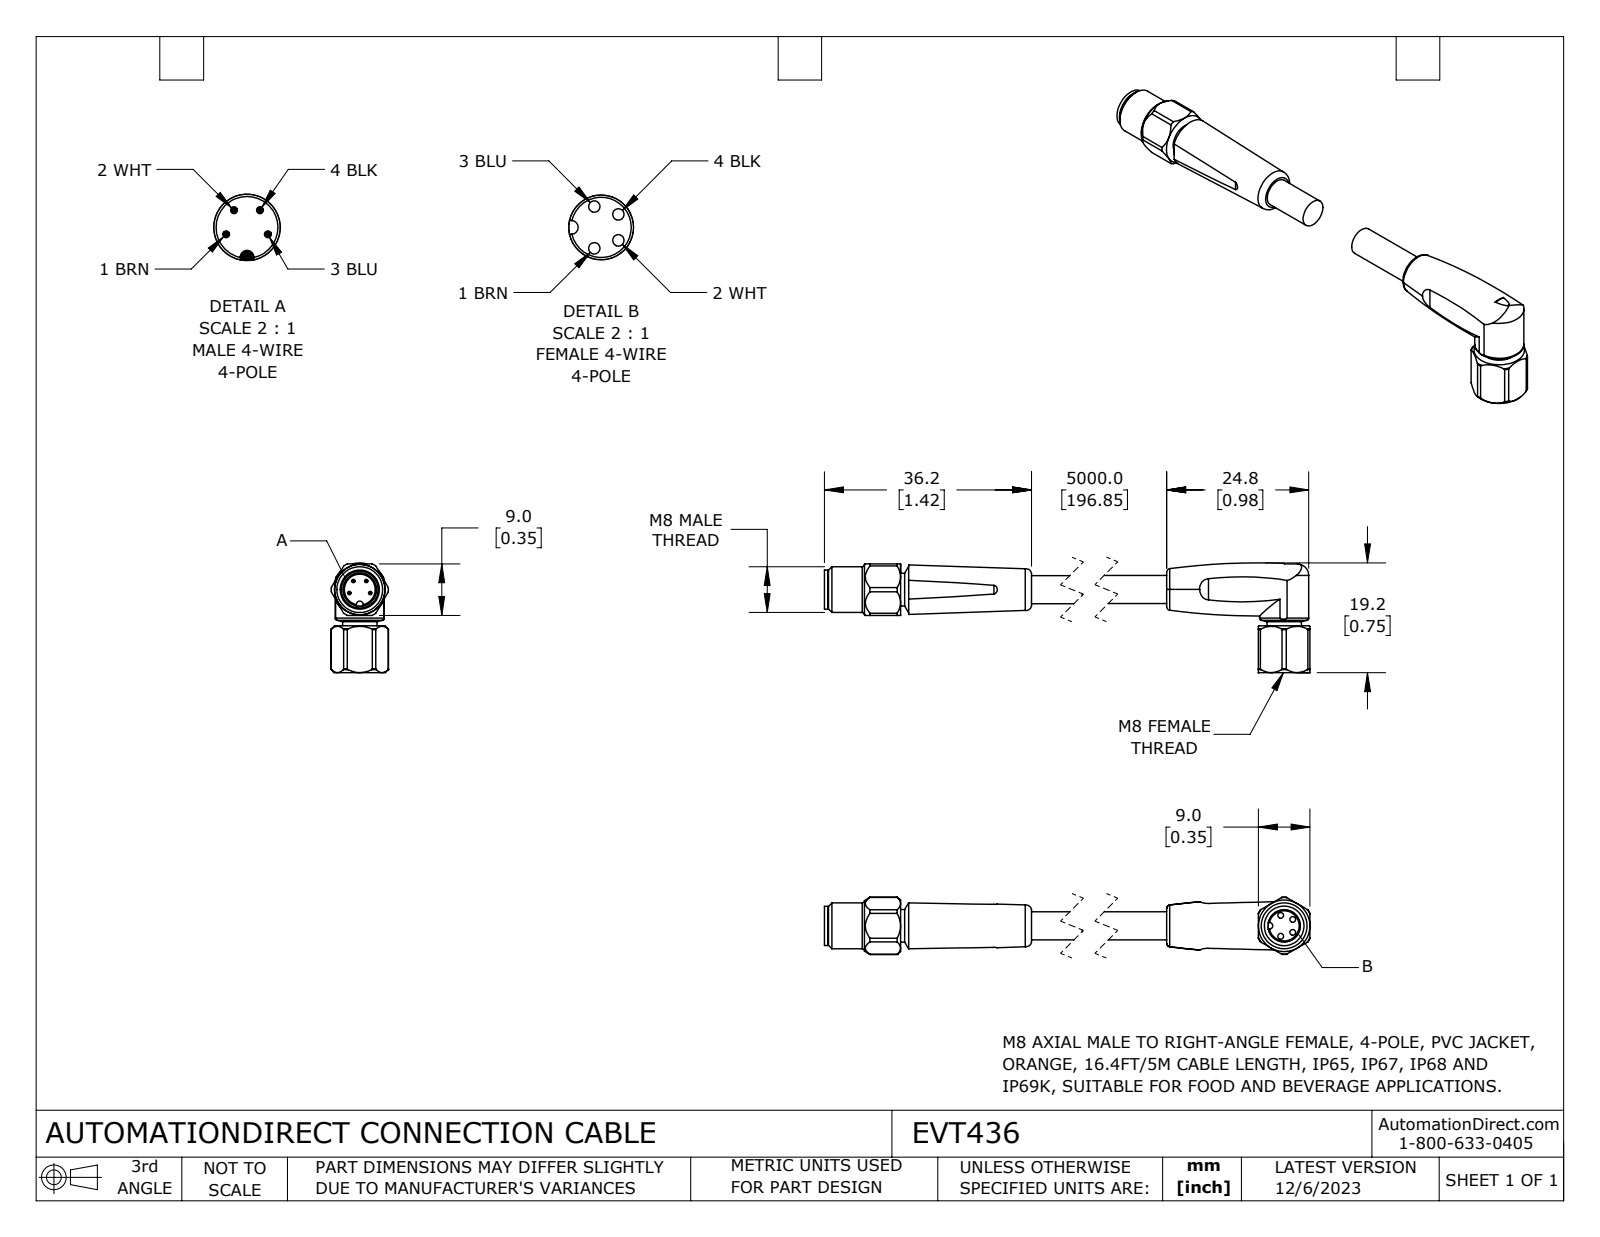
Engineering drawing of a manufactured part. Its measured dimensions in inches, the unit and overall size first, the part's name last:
Units: inches
Overall size (bounding box): 3.76 × 0.755 × 0.394
Round holes (diameter × count): ⌀0.039 ×4, ⌀0.228 ×1, ⌀0.272 ×1
Round bosses / shafts (diameter × count): ⌀0.023 ×4, ⌀0.193 ×2, ⌀0.339 ×1, ⌀0.315 ×1, ⌀0.27 ×1, ⌀0.248 ×1, ⌀0.236 ×1, ⌀0.224 ×1
Partial cylindrical surfaces — rounded edges, fillets, slot ends (radius × count): R0.024 ×2, R0.126 ×2, R0.133 ×2, R0.196 ×1, R0.197 ×1
Main face-to-face distances: 0.354, 0.354, 3.236, 2.882, 0.323, 0.748, 0.425, 0.394, 0.071, 0.327
Hole centre spacings: 0.074, 0.076, 0.087, 0.143, 0.089, 0.143
Volume: 0.254 in³ · Surface area: 4.6 in²
Bodies: 2 solids, 172 faces (52 planar, 59 cylindrical, 61 other)
Part name (STEP PRODUCT): EVT436_FEMALE; EVT436; EVT436_MALE
STEP written by: SolidWorks 2023 (CONFIG_CONTROL_DESIGN)
